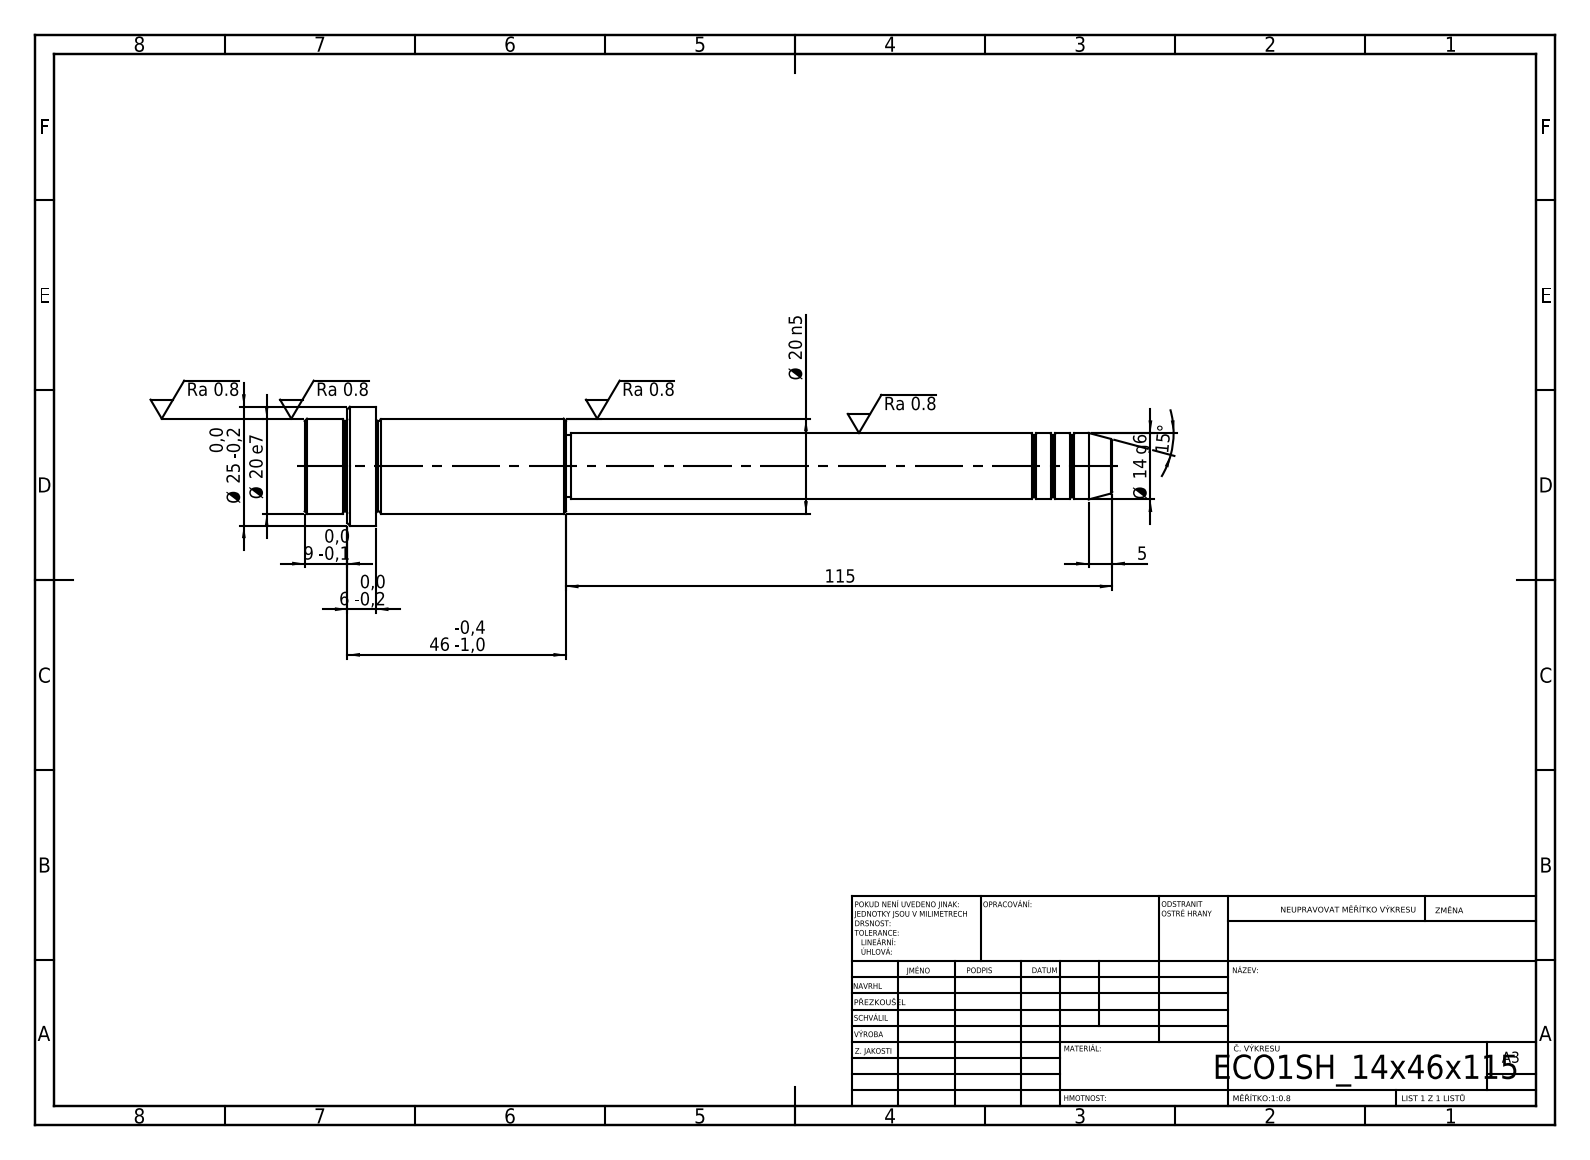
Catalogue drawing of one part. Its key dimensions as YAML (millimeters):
step_written_by: "SolidWorks 2019 (CONFIG_CONTROL_DESIGN)"
units: millimeters
bodies: {solids: 1, faces: 52, planar: 6, cylindrical: 16, other: 30}
overall_size: [170, 25, 25]
volume: 35758
surface_area: 9628
round_bosses_or_shafts:
  - {diameter: 25, count: 1}
  - {diameter: 20, count: 1}
  - {diameter: 14, count: 1}
  - {diameter: 13, count: 1}
face_to_face_distances: [15, 40, 55, 46, 6, 9, 115, 155, 161, 170]
